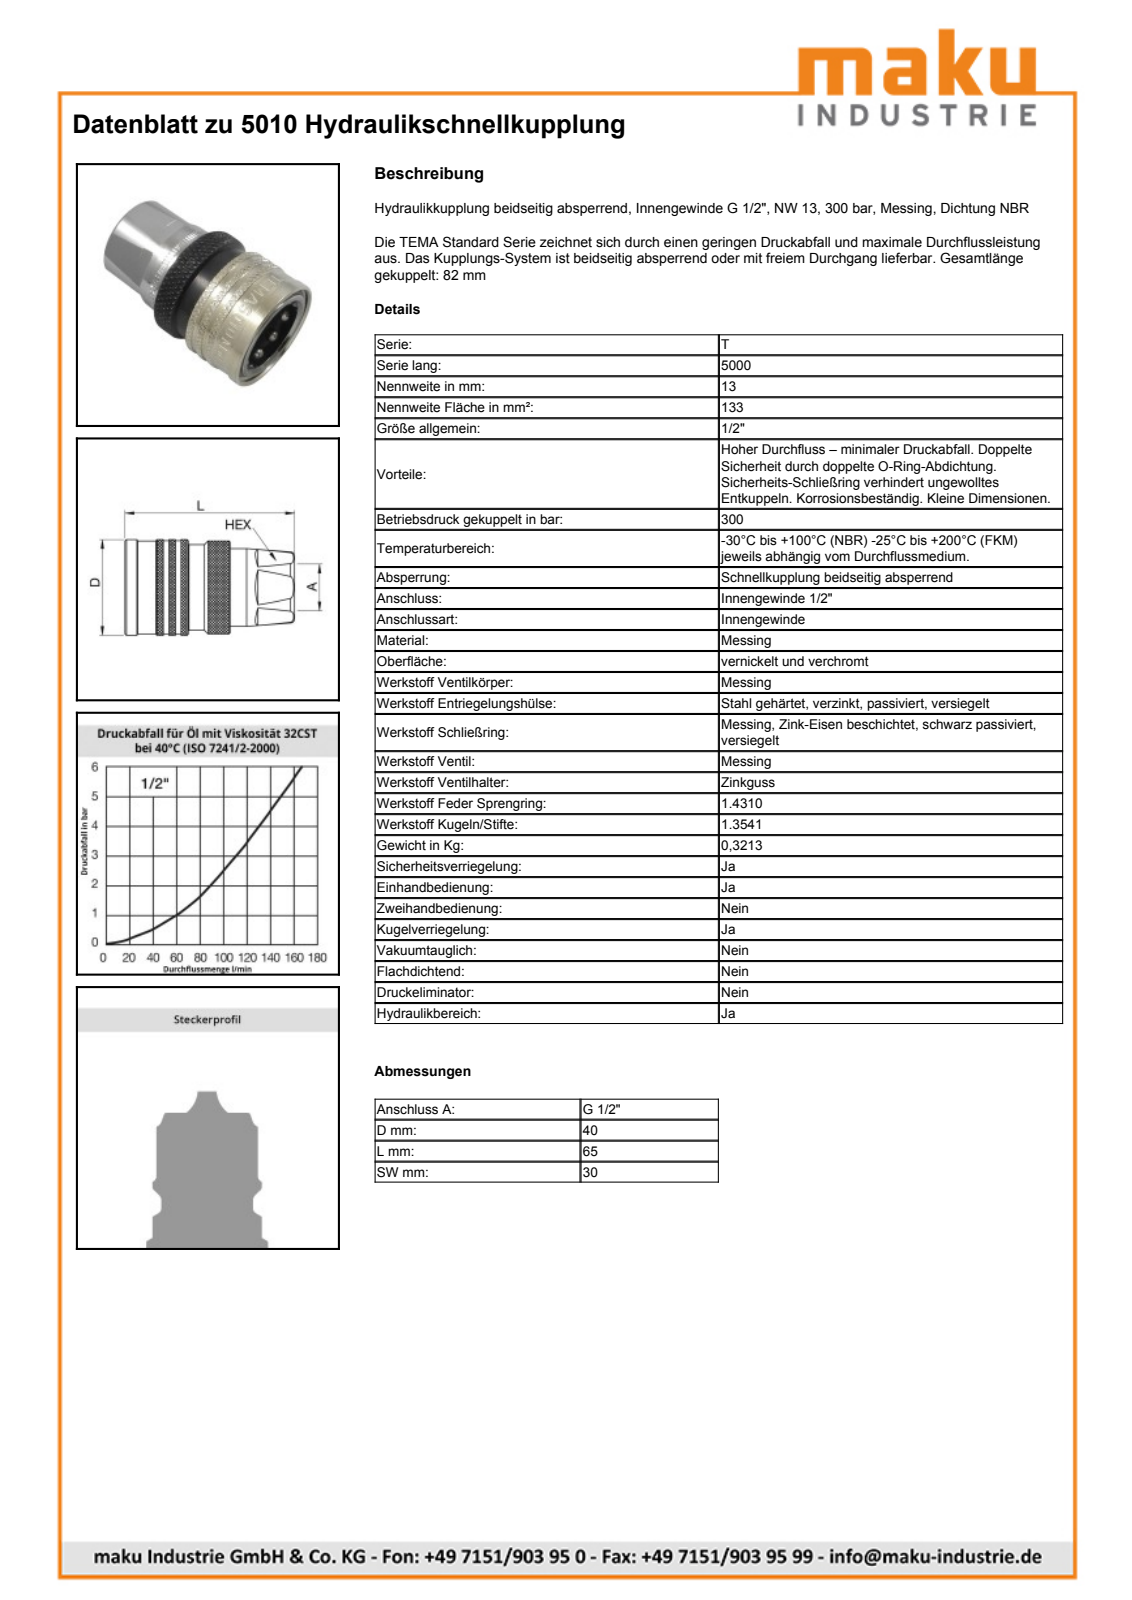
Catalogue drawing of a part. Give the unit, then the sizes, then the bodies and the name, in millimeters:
Units: millimetres
Overall size (bounding box): 65.15 × 40 × 40
Round holes (diameter × count): ⌀13.2 ×1, ⌀18.64 ×1, ⌀24.8 ×1, ⌀26.8 ×1, ⌀36.6 ×1
Round bosses / shafts (diameter × count): ⌀40 ×1, ⌀39.2 ×1, ⌀39 ×1, ⌀36.2 ×1, ⌀35.9 ×1, ⌀32.8 ×1, ⌀32.6 ×1
Main face-to-face distances: 30, 25.15, 12, 37.15, 28, 40, 65.15, 17.49, 10.51, 22.51
Volume: 47 855 mm³ · Surface area: 13 849 mm²
Bodies: 1 solid, 102 faces (26 planar, 38 cylindrical, 38 other)
Part name (STEP PRODUCT): 5010
STEP written by: SolidWorks 2009 (AUTOMOTIVE_DESIGN)
